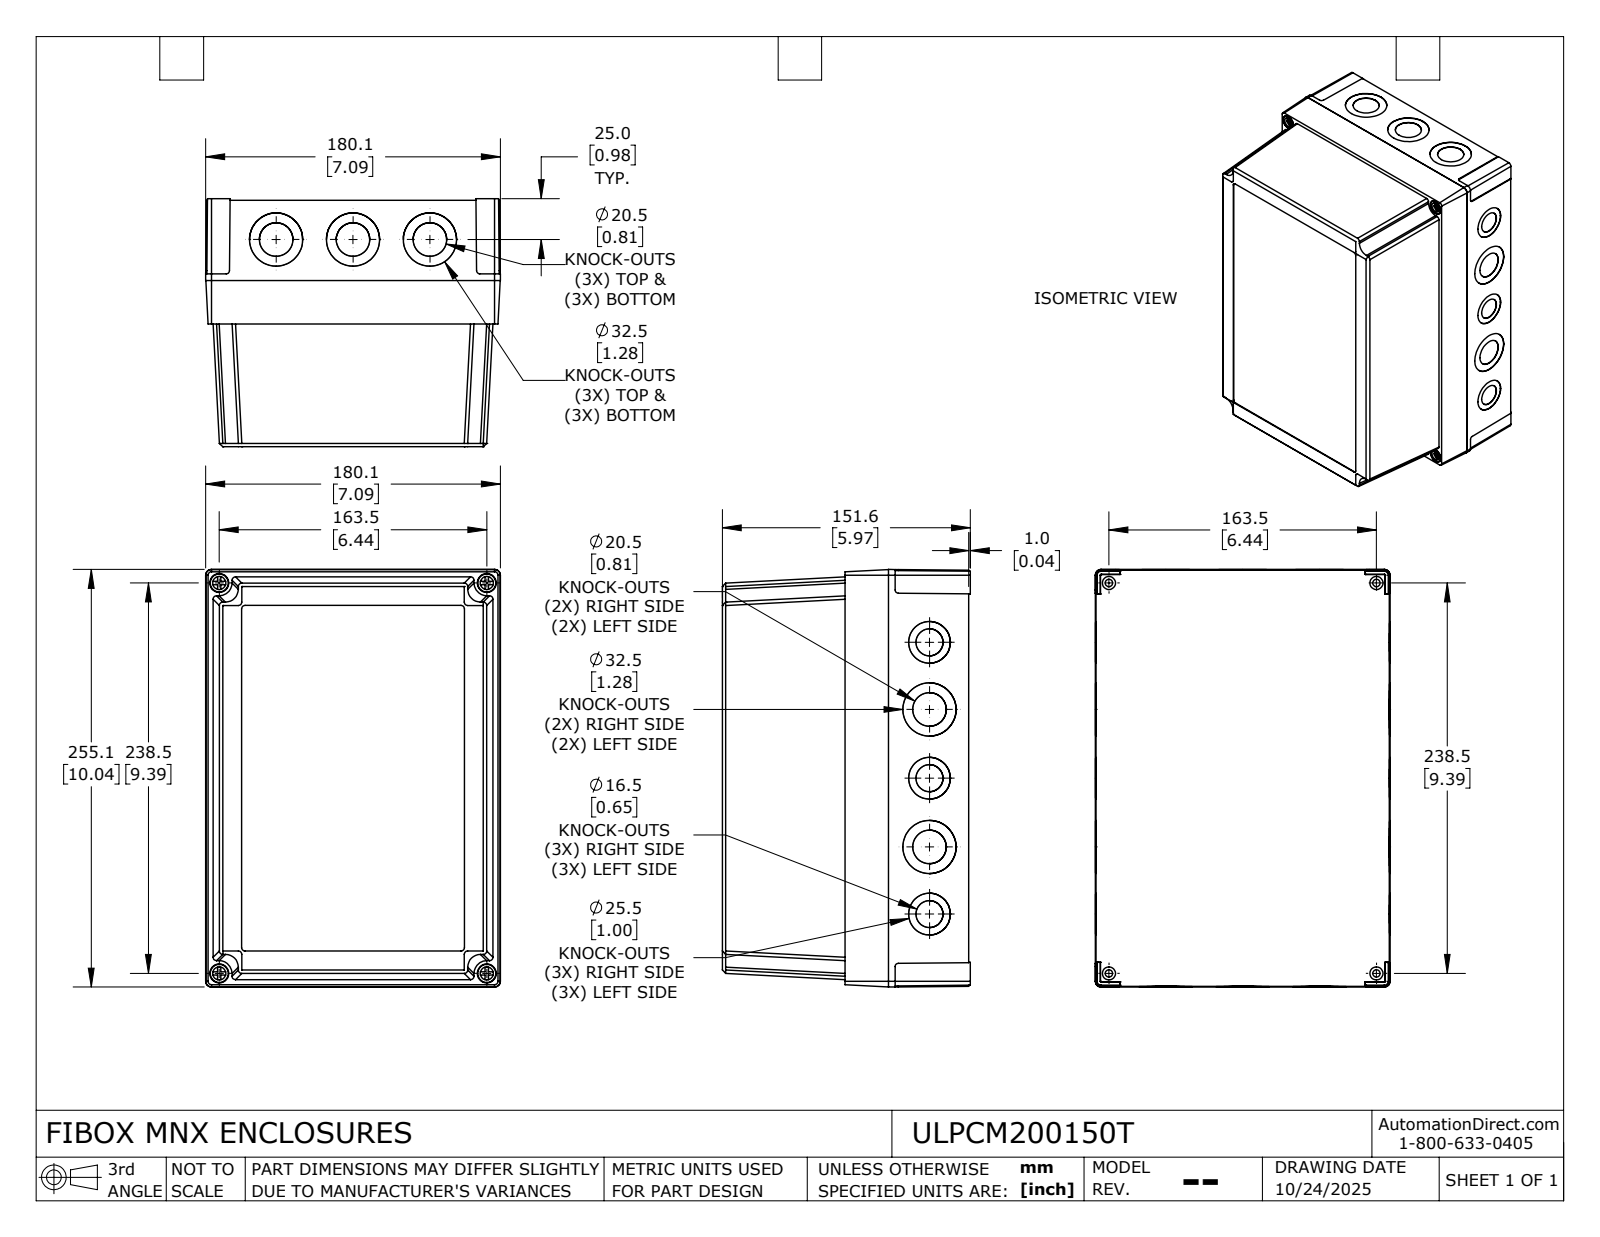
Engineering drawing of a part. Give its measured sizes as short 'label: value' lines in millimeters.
name: ULPCM200150T_Default
written by: SolidWorks 2024 (CONFIG_CONTROL_DESIGN)
unit: mm
bodies: 6 solids, 749 faces (395 planar, 296 cylindrical, 58 other)
size: 255.1 × 180.1 × 151.6
volume: 583 500 mm³; area: 438 400 mm²
holes: 20× ⌀3.2, 20× ⌀4, 10× ⌀20.5, 10× ⌀32.5, 6× ⌀16.5, 6× ⌀25.5, 4× ⌀4.5, 4× ⌀8, 4× ⌀11.6
bosses: 16× ⌀8, 4× ⌀11, 4× ⌀7.2, 4× ⌀7
rounds: 8× R2, 8× R2.1, 6× R2.8, 4× R1.1, 4× R5, 4× R7.8, 2× R1.2
face distances: 1.5, 3, 147.6, 144.6, 2.5, 150.1, 147.1, 4.2, 4.6, 3
hole spacings: 125, 49.3, 128.2, 20.6, 22.1, 26.6, 33.9, 38.3
